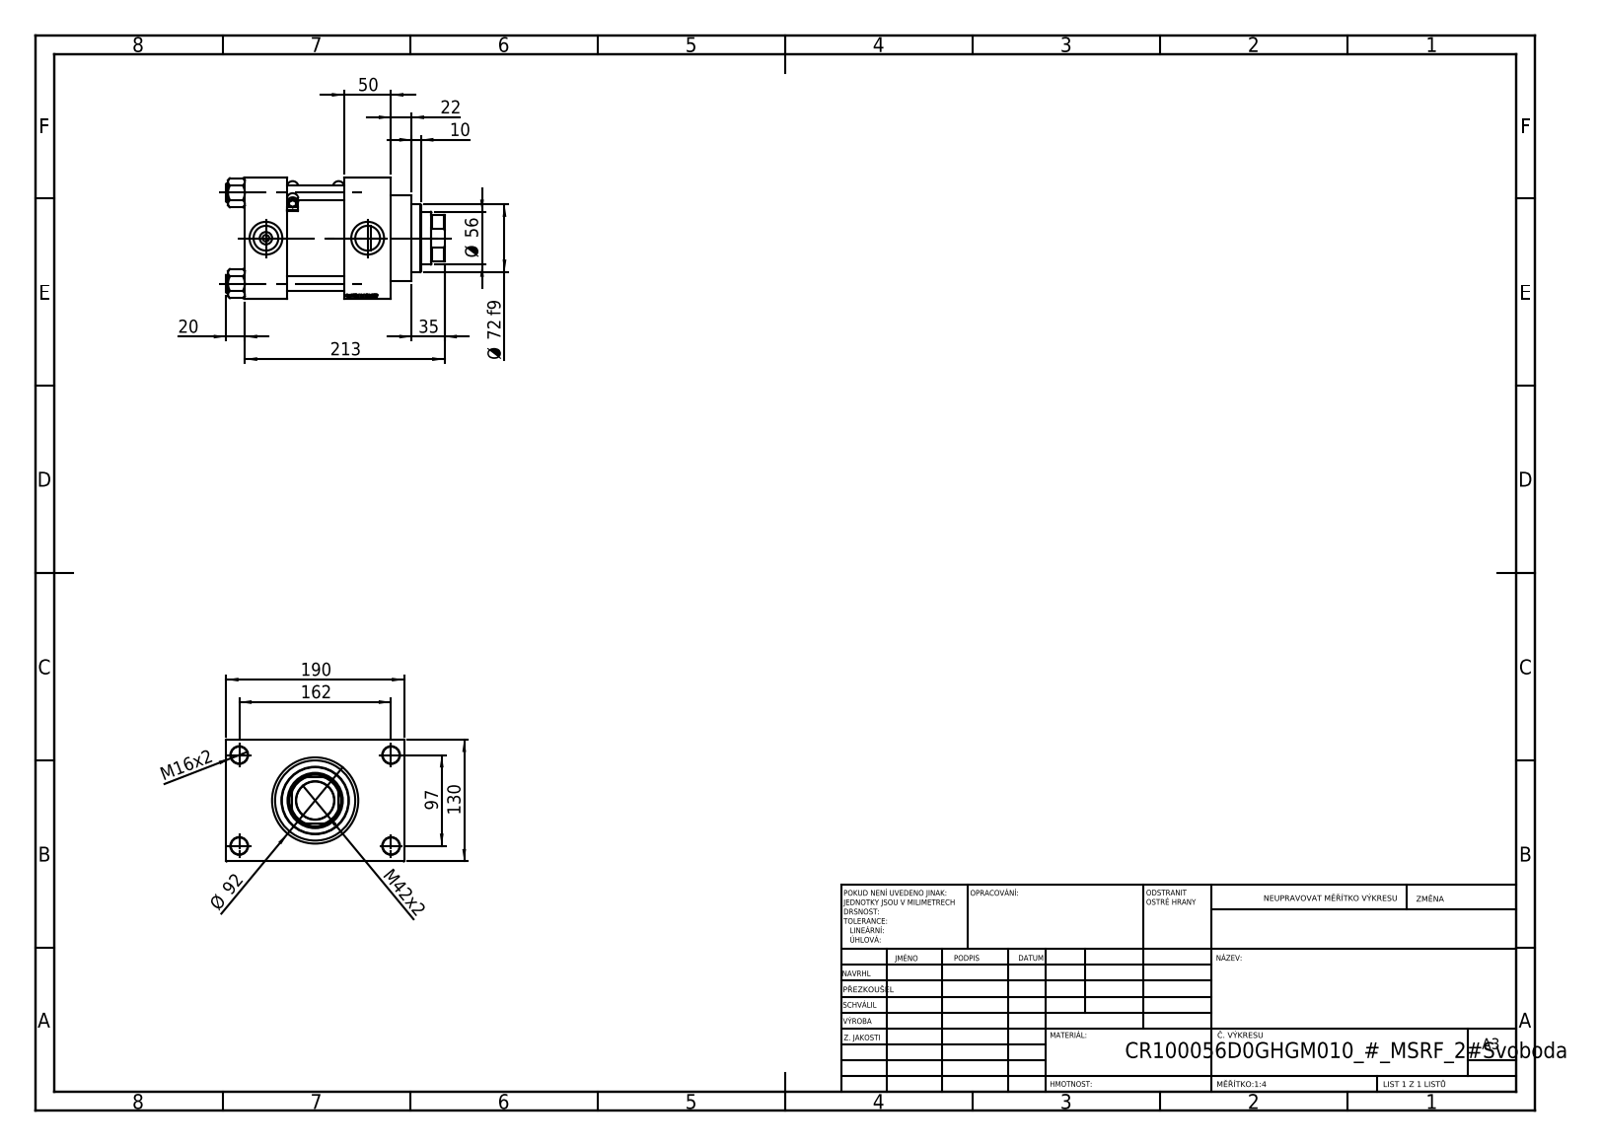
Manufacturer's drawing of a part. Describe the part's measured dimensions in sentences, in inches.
The part is named "V215CR_D_Body; V215CR_VCP_D; V215CR_D_TYCINKA; MSRF_MSRG1 (+2 more)". Its 3-D file was written by "SolidWorks 2019 (CONFIG_CONTROL_DESIGN)". It is 13 solids with 1215 faces: 581 planar, 116 cylindrical and 518 other. Overall it measures 9.173 by 7.48 by 5.118 inches. Its volume is 158.2 cubic inches and its surface area 553.1 square inches. Round holes: 4 of diameter 0.63, 4 of diameter 0.709, 2 of diameter 0.276, 2 of diameter 1.041, 2 of diameter 1.378, 1 of diameter 1.594, 1 of diameter 2.205, 1 of diameter 2.323, 1 of diameter 2.992, 1 of diameter 3.366, 1 of diameter 3.937. Round bosses or shafts: 4 of diameter 0.748, 2 of diameter 0.197, 2 of diameter 0.098, 1 of diameter 4.173, 1 of diameter 3.622, 1 of diameter 2.835. Partial cylindrical surfaces (rounded edges, fillets, slot ends): 12 of radius 0.02, 4 of radius 0.236, 1 of radius 1.063. The main face-to-face distances are 5.118, 1.969, 1.772, 4.173, 2.402, 6.142, 4.37, 1.181, 6.299, 0.394. The hole center spacings are 1.281, 2.698, 3.717, 3.815, 4.026, 5.096, 6.367, 3.819.
